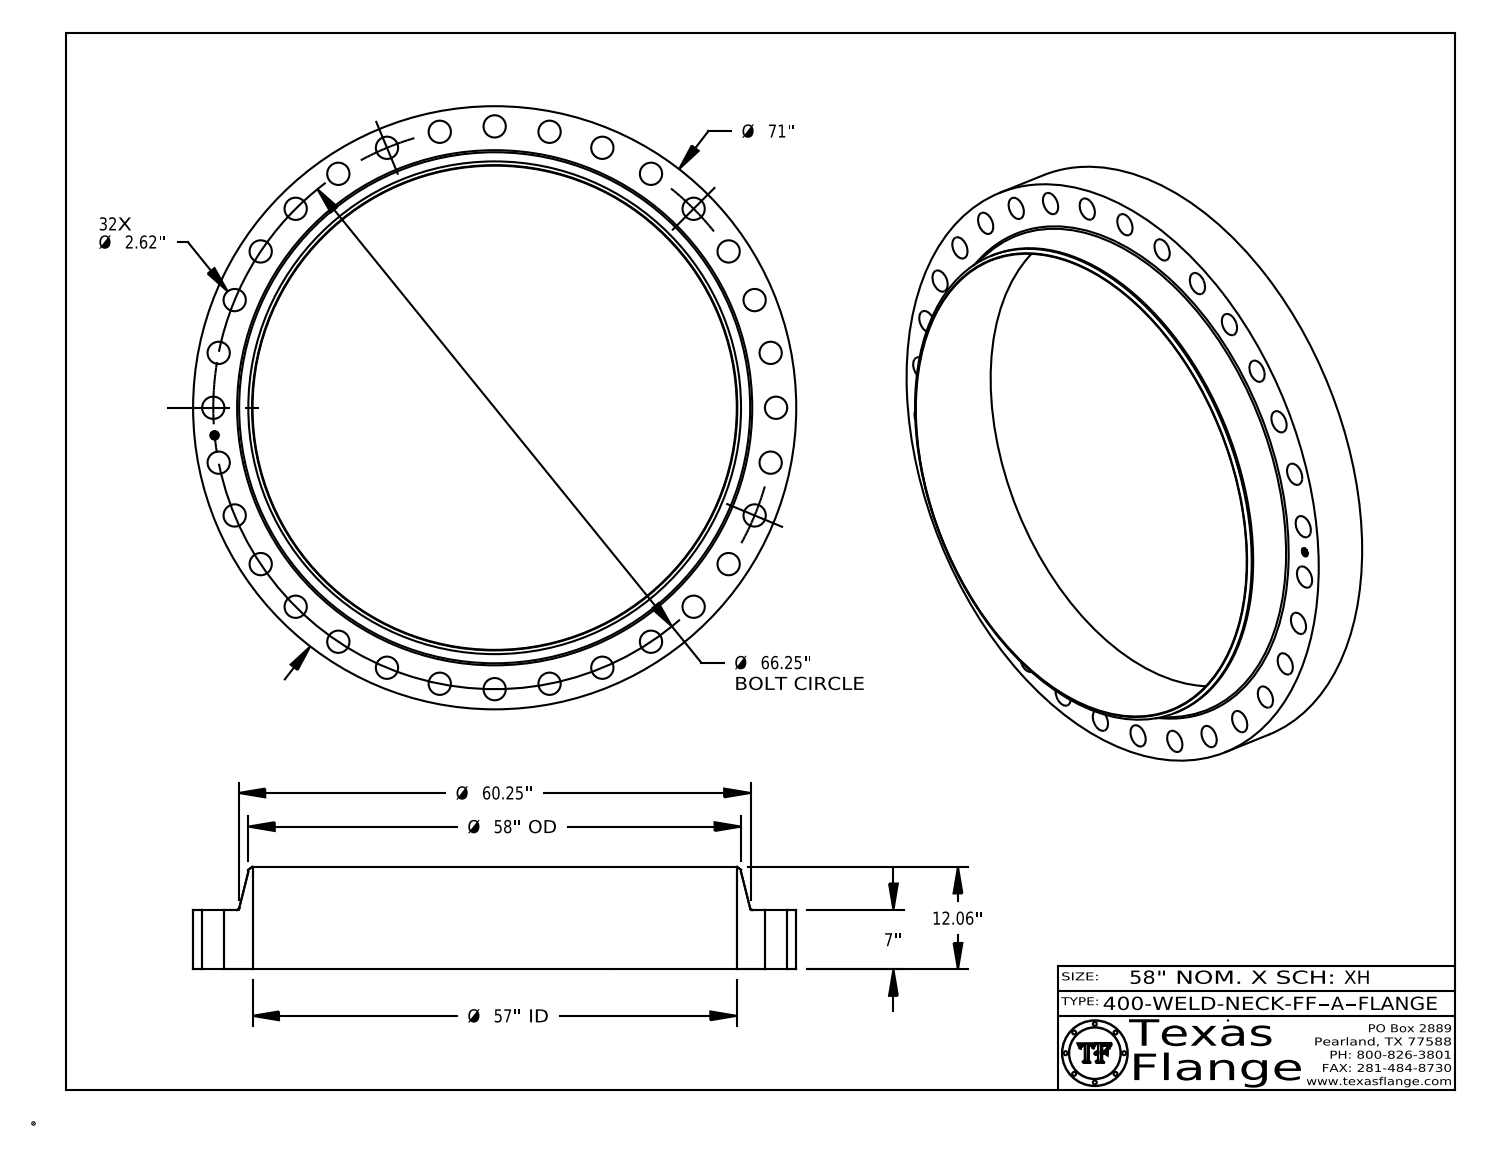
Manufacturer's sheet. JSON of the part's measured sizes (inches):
{"part_name": "400-WELD-NECK-FF, Series A", "step_written_by": "CATIA V5 STEP AP214 (AUTOMOTIVE_DESIGN)", "units": "inches", "bodies": {"solids": 1, "faces": 464, "planar": 368, "cylindrical": 90, "other": 6}, "overall_size": [71, 71, 12.06], "volume_in3": 9555, "surface_area_in2": 8738, "round_holes": [[2.62, 32], [1, 1], [57, 1]], "round_bosses_or_shafts": [[0.061, 8], [71, 1], [58, 1], [0.788, 1]], "face_to_face_distances": [7, 12.06, 5.06, 0.015, 6.985, 5.075, 0.298, 0.292, 0.054, 0.193], "hole_center_spacings": [61.207, 33.125, 6.494, 12.925, 46.846, 63.397, 65.931, 64.977]}
